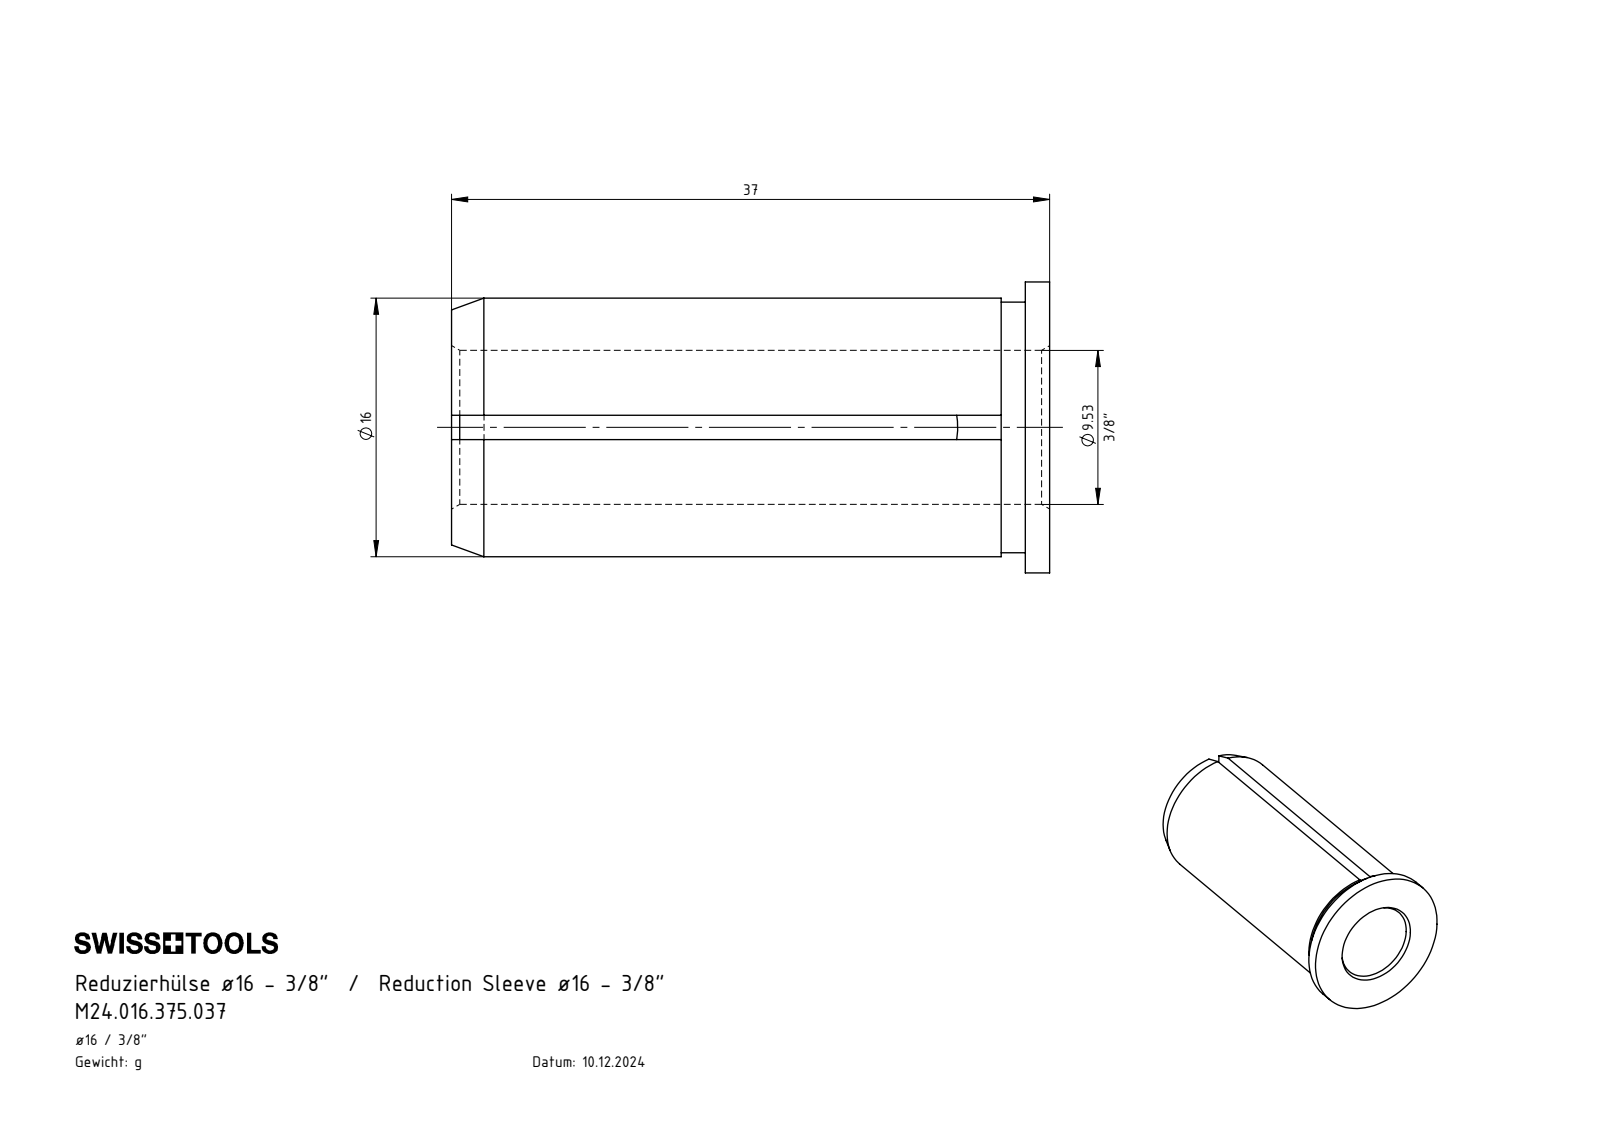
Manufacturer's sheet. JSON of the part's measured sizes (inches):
{"part_name": "M24.016.375.037", "step_written_by": "SolidWorks 2022 (CONFIG_CONTROL_DESIGN)", "units": "inches", "bodies": {"solids": 1, "faces": 24, "planar": 6, "cylindrical": 10, "other": 8}, "overall_size": [1.457, 0.709, 0.709], "volume_in3": 0.285, "surface_area_in2": 5.326, "round_holes": [[0.375, 1]], "round_bosses_or_shafts": [[0.709, 1], [0.63, 1], [0.61, 1]], "partial_cylinders_radius": [[1.24, 1]], "face_to_face_distances": [0.059, 1.457, 1.398, 1.339, 0.118]}
